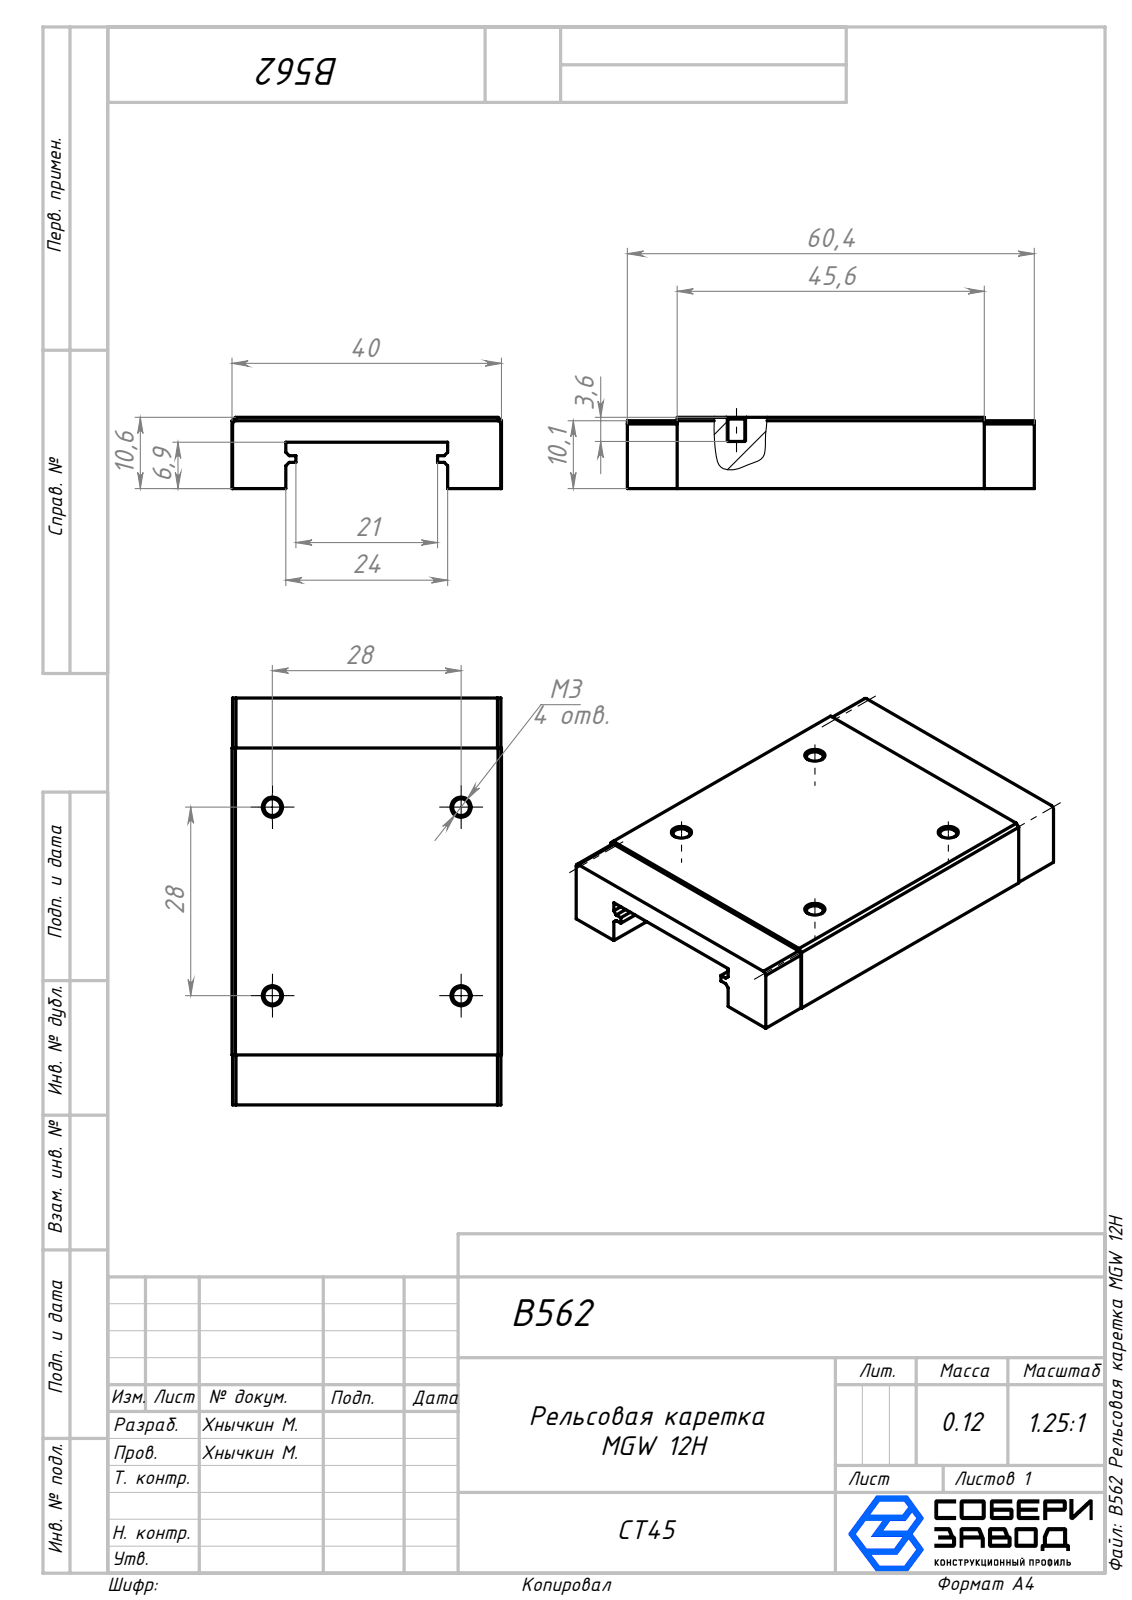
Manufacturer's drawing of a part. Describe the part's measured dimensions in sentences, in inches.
The part is named "B562 Рельсовая каретка MGW 12H". Its 3-D file was written by "SolidWorks 2026 (AUTOMOTIVE_DESIGN)". It is 1 solid with 56 faces: 36 planar, 12 cylindrical and 8 other. Overall it measures 2.378 by 1.575 by 0.417 inches. Its volume is 0.94 cubic inches and its surface area 12.11 square inches. Round holes: 4 of diameter 0.098. Partial cylindrical surfaces (rounded edges, fillets, slot ends): 2 of radius 0.02. The main face-to-face distances are 0.146, 0.272, 0.417, 0.315, 1.26, 0.398, 0.126, 0.02, 1.575, 0.945. The hole center spacings are 1.102, 1.559.
